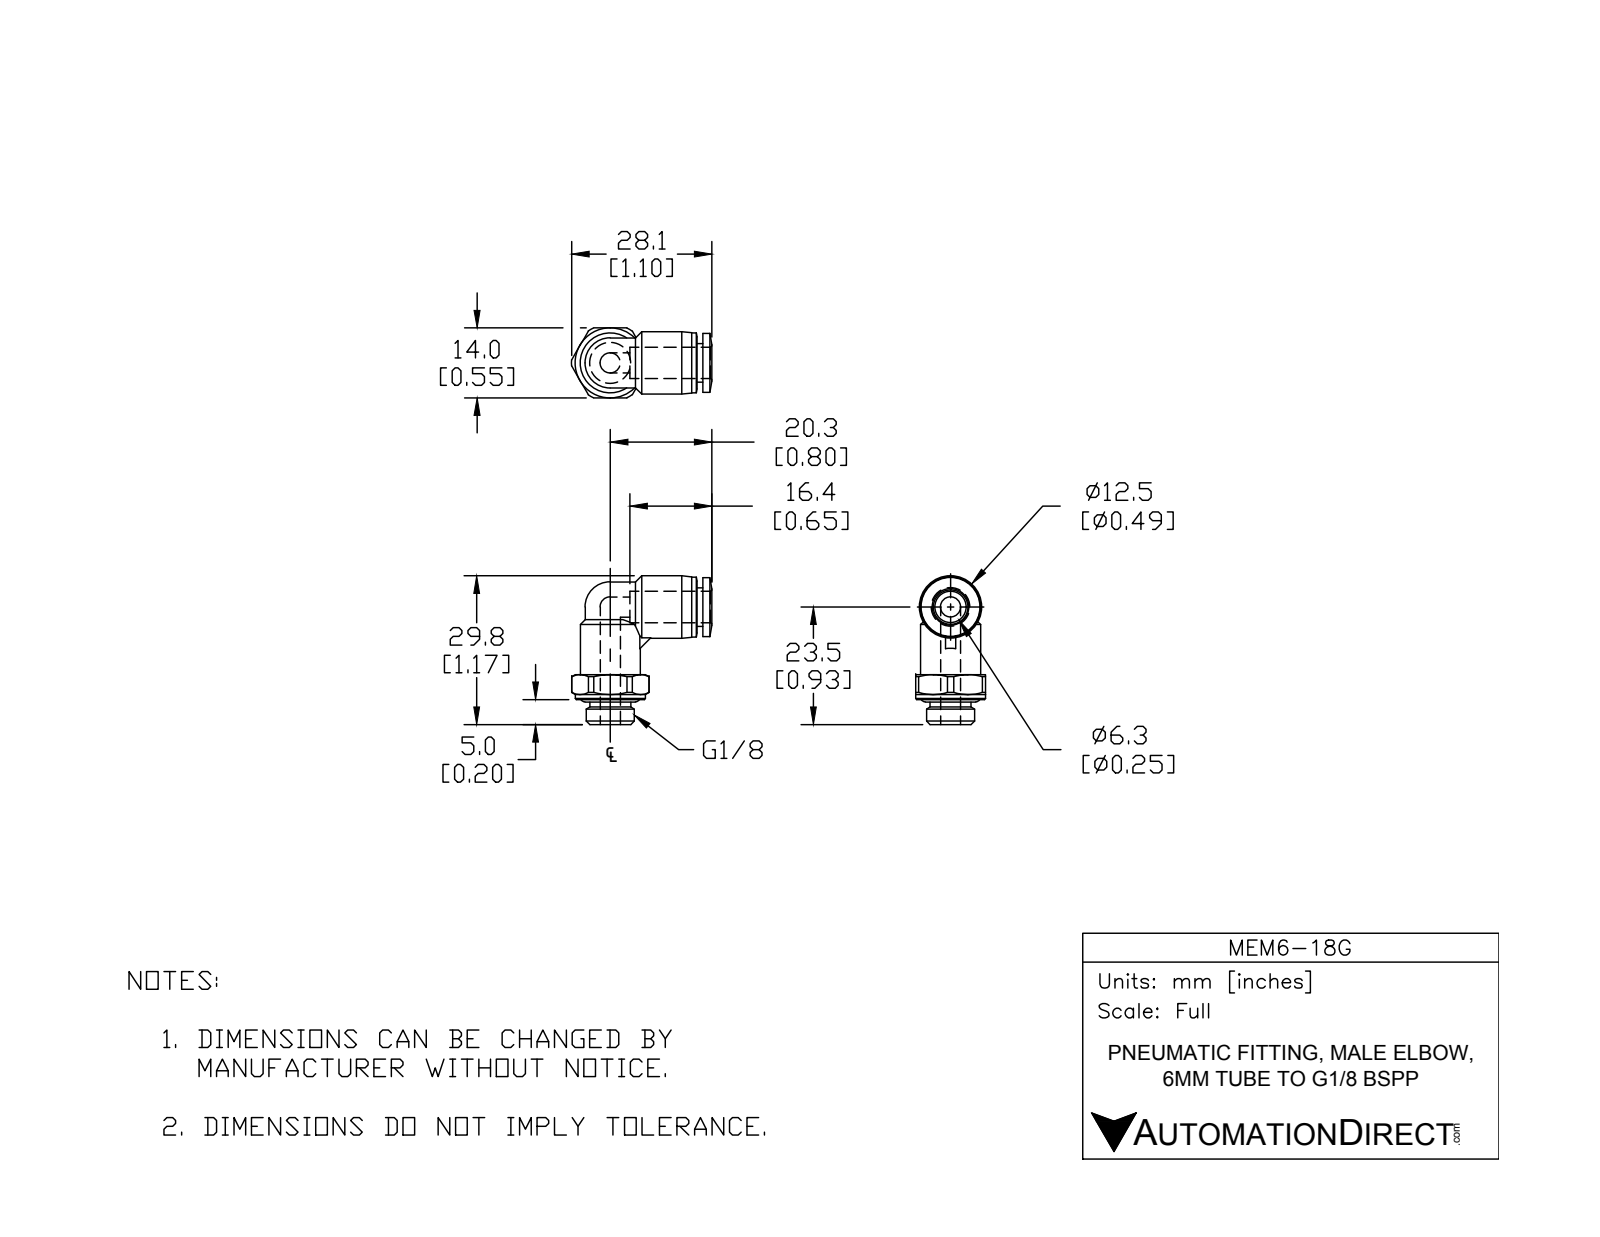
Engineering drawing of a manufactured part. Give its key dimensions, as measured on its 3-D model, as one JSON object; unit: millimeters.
{"part_name": "ME6M-18G", "step_written_by": "SolidWorks 2015 (AUTOMOTIVE_DESIGN)", "units": "millimeters", "bodies": {"solids": 2, "faces": 90, "planar": 18, "cylindrical": 33, "other": 39}, "overall_size": [29.7, 28, 14], "volume_mm3": 3770, "surface_area_mm2": 2926, "round_holes": [[4, 2], [6.3, 1]], "round_bosses_or_shafts": [[12, 2], [14, 1], [12.5, 1], [11.8, 1], [9.6, 1], [8.2, 1], [7.7, 1]], "partial_cylinders_radius": [[5, 2], [7.7, 1]], "face_to_face_distances": [14, 3.6, 6.4, 10, 1.1, 5, 13.5, 14.6, 1.4, 6]}
